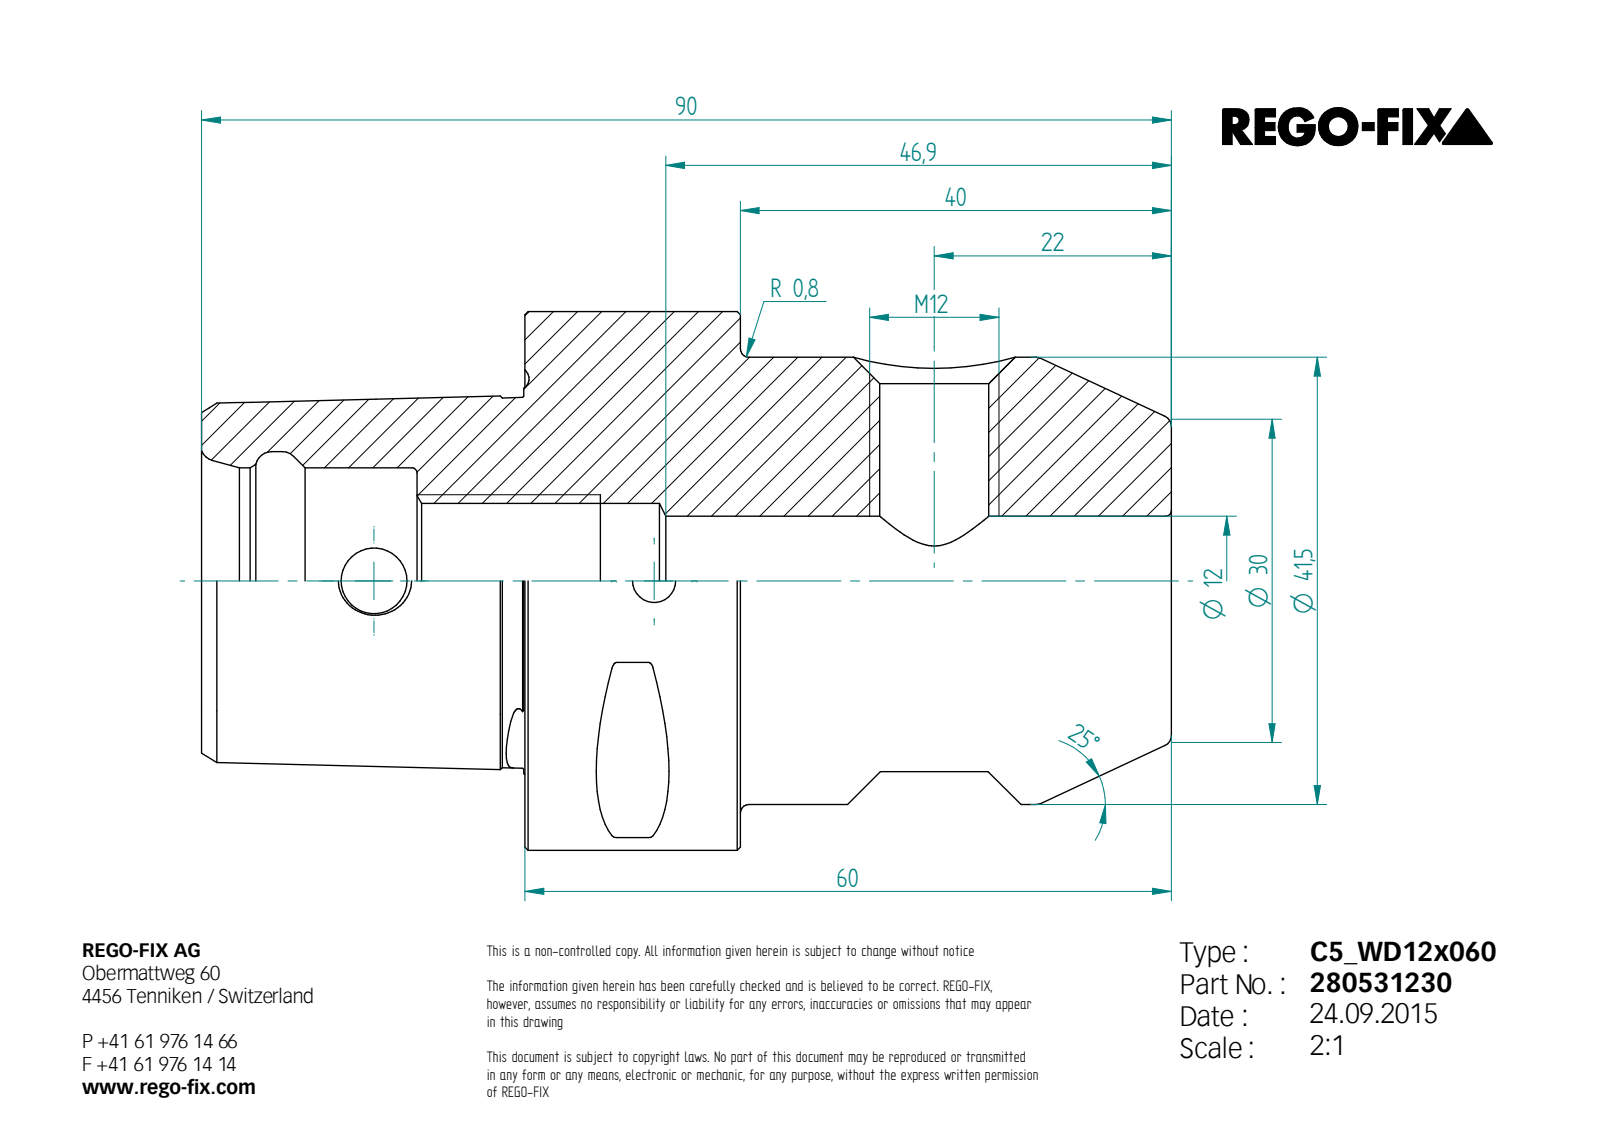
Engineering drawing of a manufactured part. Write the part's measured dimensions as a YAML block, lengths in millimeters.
step_written_by: "Unknown (AUTOMOTIVE_DESIGN)"
units: millimeters
bodies: {solids: 1, faces: 96, planar: 23, cylindrical: 20, other: 53}
overall_size: [90, 50, 50]
volume: 96870
surface_area: 19144
round_holes:
  - {diameter: 4, count: 1}
  - {diameter: 6.1, count: 1}
  - {diameter: 10.11, count: 1}
  - {diameter: 12, count: 1}
  - {diameter: 14.38, count: 1}
  - {diameter: 21, count: 1}
  - {diameter: 24, count: 1}
round_bosses_or_shafts:
  - {diameter: 50, count: 1}
  - {diameter: 41.5, count: 1}
partial_cylinders:
  - {radius: 0.5, count: 8}
face_to_face_distances: [20, 60, 40, 30, 50, 90, 19.18, 44.4, 10, 70]
hole_center_spacings: [26]
